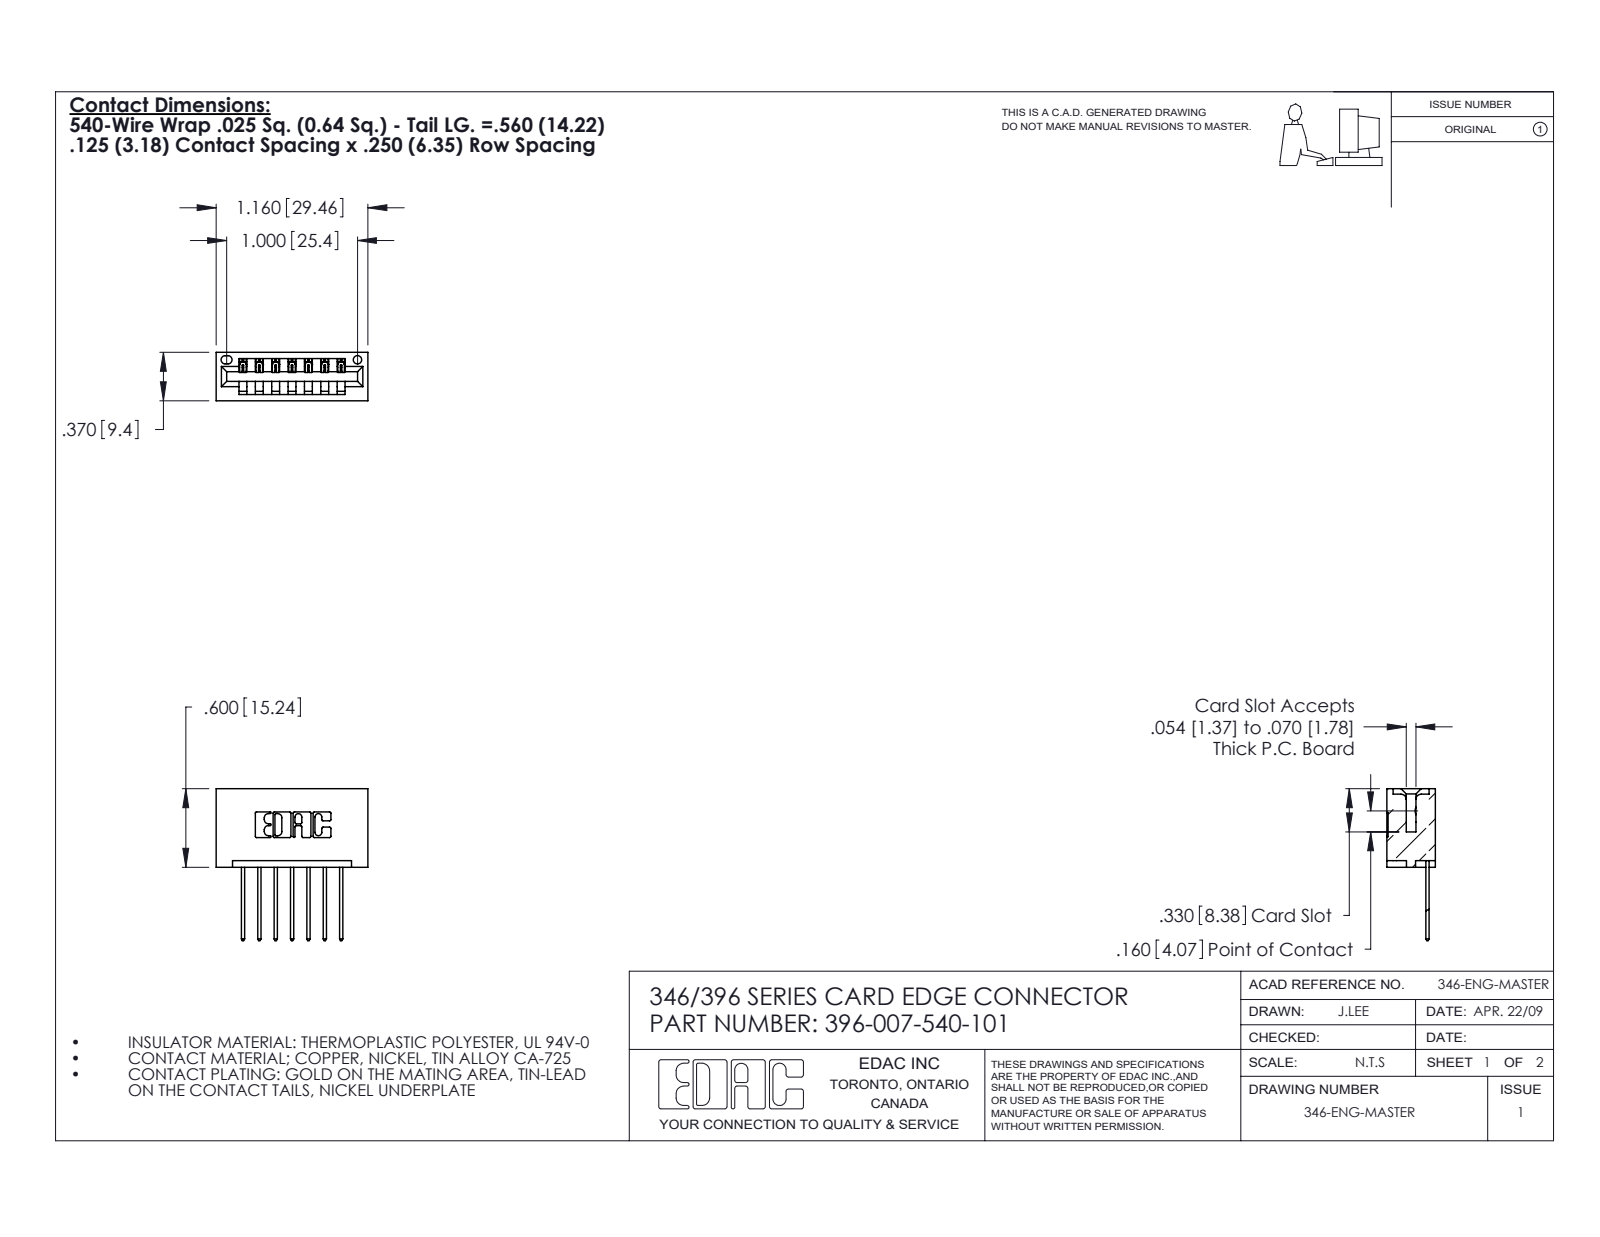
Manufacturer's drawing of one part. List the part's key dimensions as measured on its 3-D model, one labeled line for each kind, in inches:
Part name (STEP PRODUCT): 346 Part_No Mounting Lugs; 345-292-001_345-293-140; 396-007-540-101
STEP written by: SolidWorks 2020 (CONFIG_CONTROL_DESIGN)
Units: inches
Bodies: 8 solids, 520 faces (352 planar, 168 cylindrical, 0 other)
Overall size (bounding box): 1.16 × 1.16 × 0.37
Volume: 0.191 in³ · Surface area: 5.718 in²
Round holes (diameter × count): ⌀0.064 ×1
Partial cylindrical surfaces — rounded edges, fillets, slot ends (radius × count): R0.01 ×22, R0.006 ×14, R0.01 ×14, R0.007 ×6, R0.031 ×6, R0.026 ×3, R0.031 ×2, R0.04 ×2
Main face-to-face distances: 0.25, 0.048, 0.322, 0.37, 0.072, 0.298, 0.025, 0.125, 0.148, 0.222
